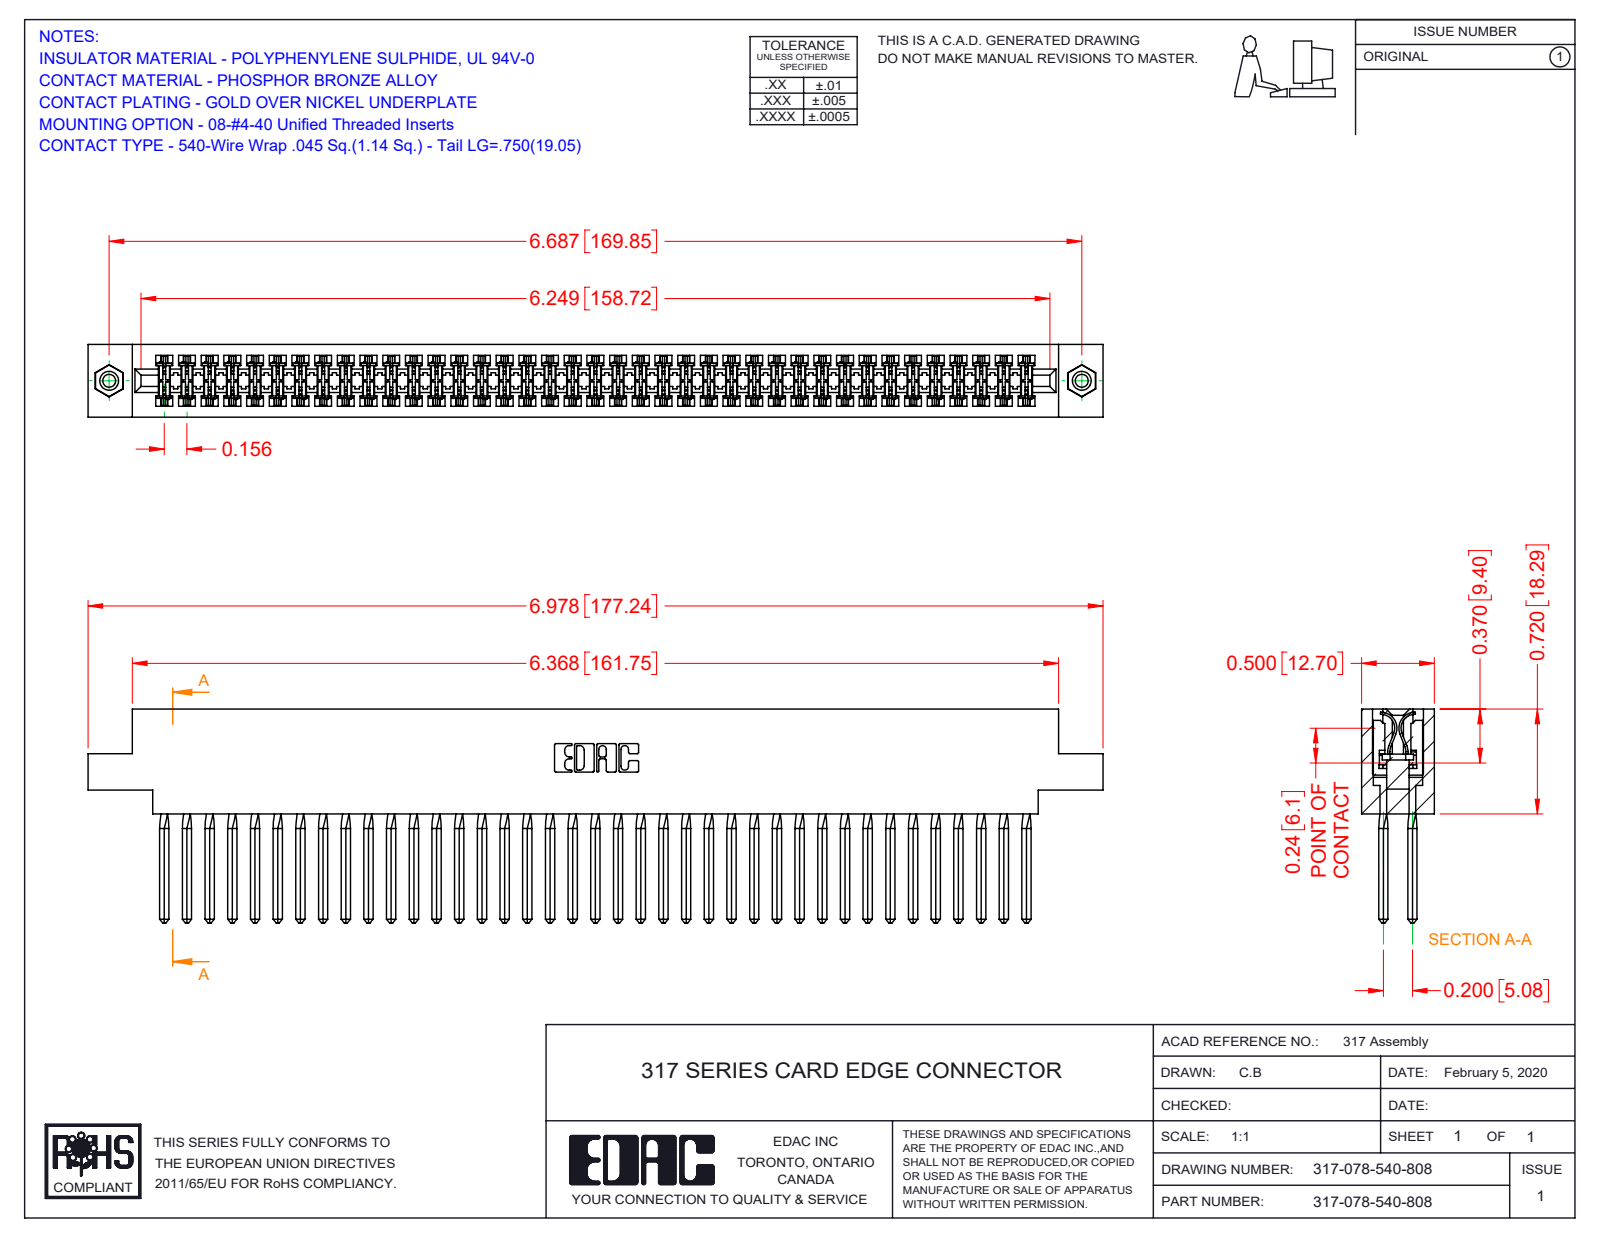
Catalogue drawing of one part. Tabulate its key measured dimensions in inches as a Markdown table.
| quantity | value |
| --- | --- |
| part name | 317-078-540-878; 345-250-001_345-250-003-102; 317 Part_.156 Dia - TI; 317-290-001_540 |
| STEP written by | SolidWorks 2016 (CONFIG_CONTROL_DESIGN) |
| units | inches |
| bodies | 81 solids, 7104 faces (5784 planar, 992 cylindrical, 328 other) |
| overall size | 6.978 × 1.47 × 0.5 |
| volume | 1.809 in³ |
| surface area | 68.35 in² |
| round holes (diameter × count) | 0.089 × 2, 0.125 × 2, 0.156 × 2 |
| round bosses / shafts (diameter × count) | 0.155 × 2 |
| partial cylindrical surfaces (radius × count) | 0.015 × 156, 0.01 × 22, 0.007 × 6, 0.031 × 6, 0.026 × 3, 0.095 × 2, 0.1 × 2, 0.11 × 2 |
| main face-to-face distances | 0.5, 0.075, 0.425, 0.35, 0.195, 0.094, 0.2, 0.115, 0.131, 0.11 |
| hole center spacings | 6.687 |
